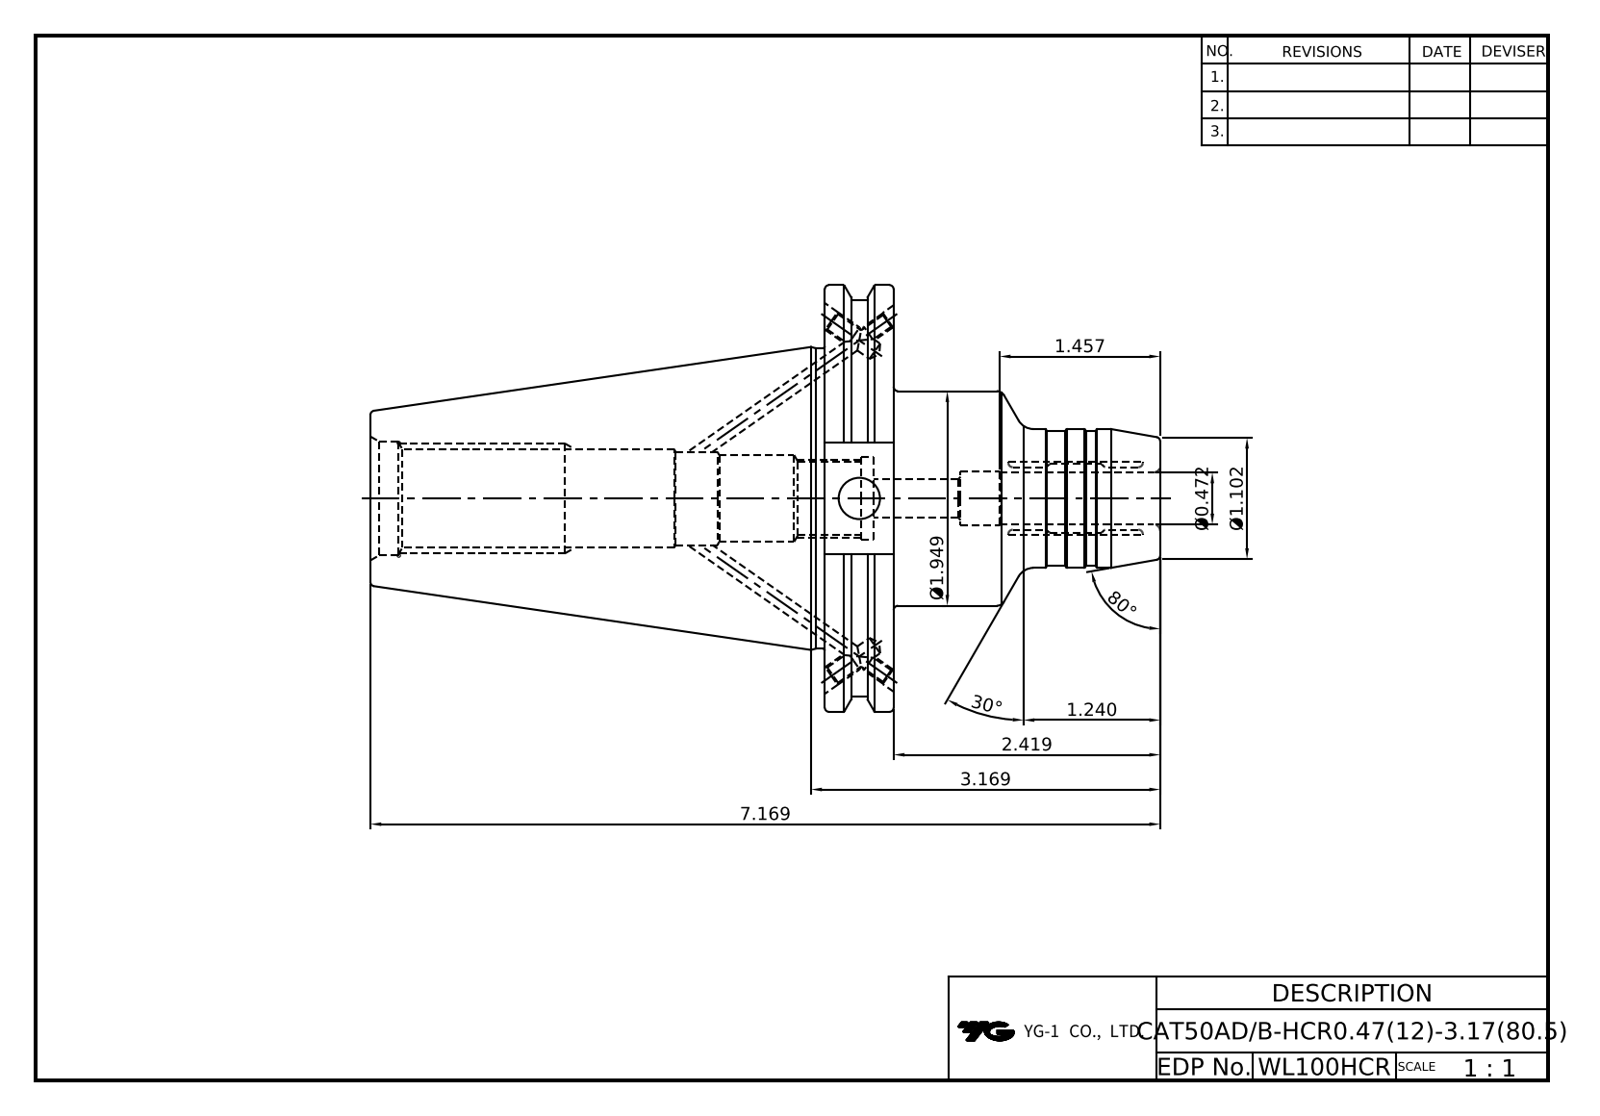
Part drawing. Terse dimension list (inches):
name: LO-CAT50ADB-HCR12-80.5
written by: Autodesk Inventor 2025 (AUTOMOTIVE_DESIGN)
unit: in
bodies: 1 solid, 106 faces (35 planar, 34 cylindrical, 37 other)
size: 7.169 × 3.875 × 3.728
volume: 23.98 in³; area: 84.62 in²
holes: 4× ⌀0.163, 4× ⌀0.197, 1× ⌀0.362, 1× ⌀0.375, 1× ⌀0.472, 1× ⌀0.496, 1× ⌀0.666, 1× ⌀0.748, 1× ⌀0.846, 1× ⌀0.865, 1× ⌀1.031
bosses: 1× ⌀3.875, 1× ⌀3.594, 1× ⌀2.726, 1× ⌀1.949, 1× ⌀1.26, 1× ⌀1.22
face distances: 0.625, 4.125, 4.75, 7.169, 3.044, 2.419, 2.875, 1.02, 4.571, 0.446
hole spacings: 2.35
